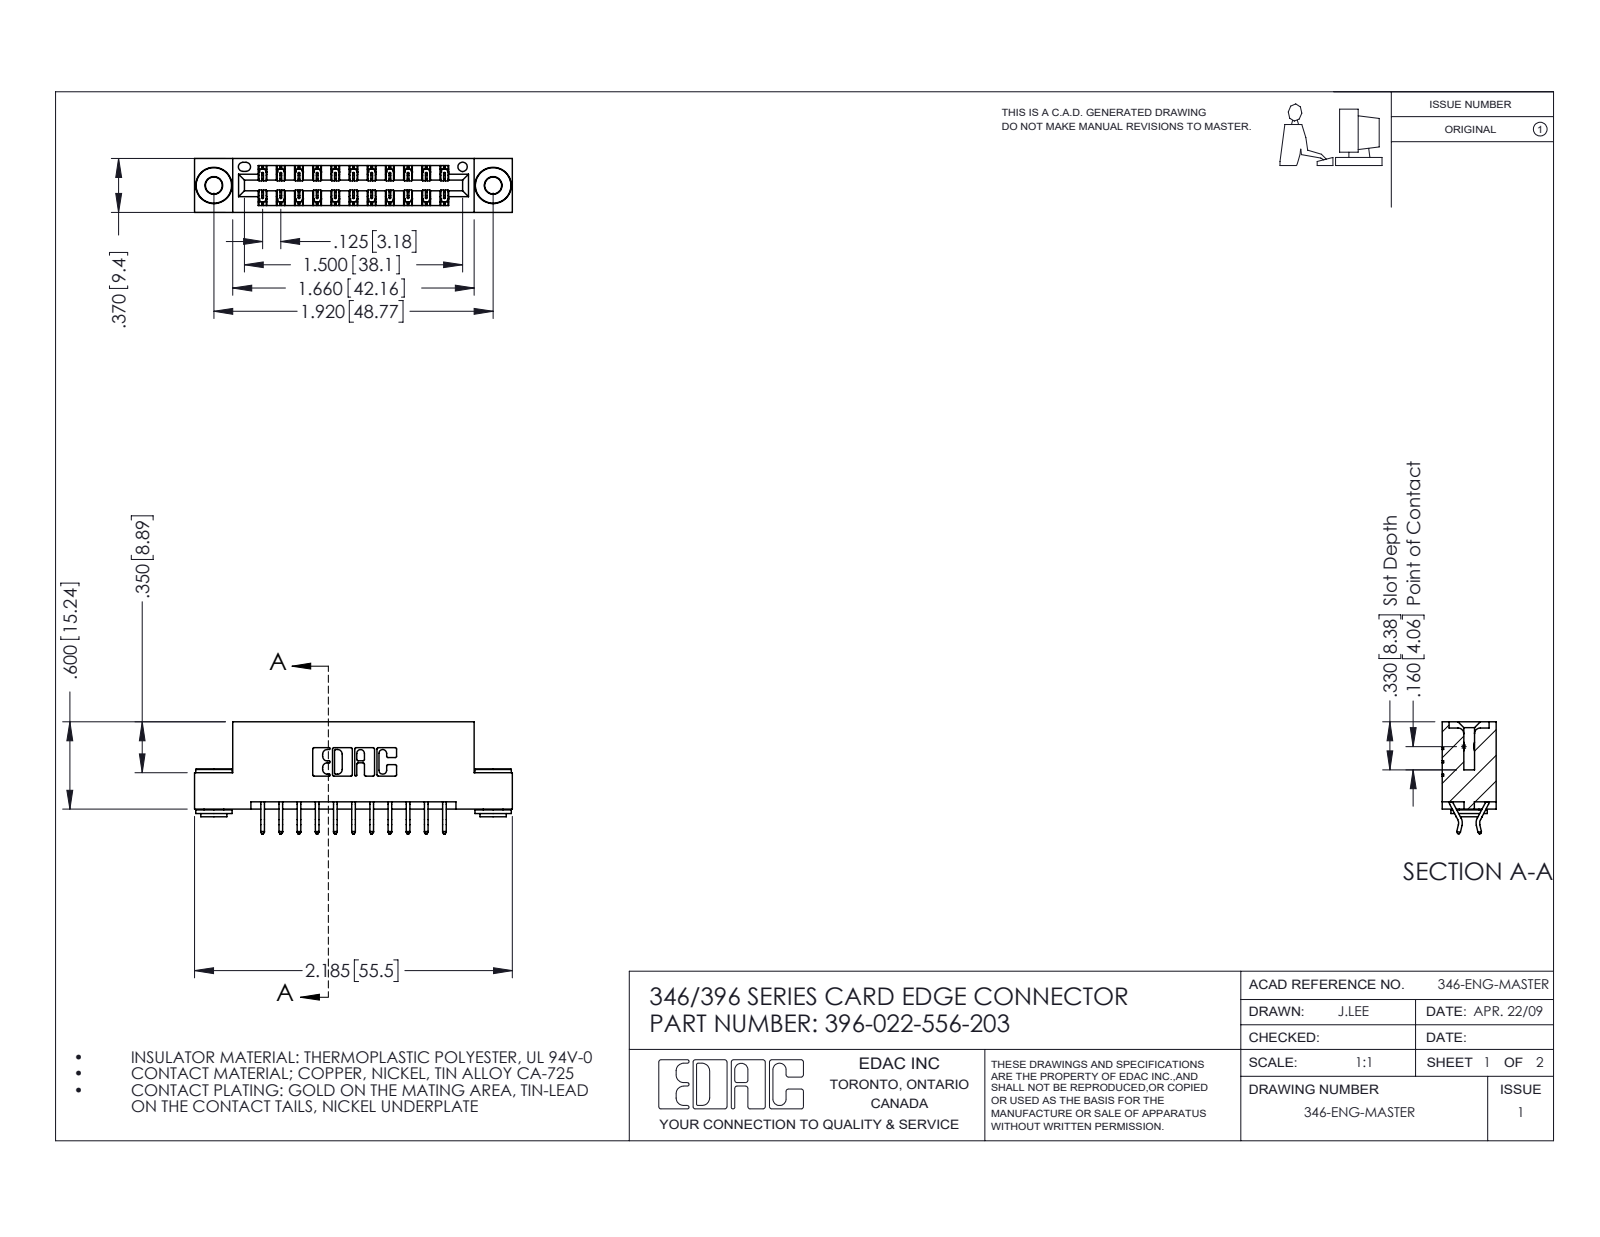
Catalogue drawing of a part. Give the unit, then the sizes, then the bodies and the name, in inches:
Units: inches
Overall size (bounding box): 2.185 × 0.77 × 0.37
Round holes (diameter × count): ⌀0.116 ×2, ⌀0.156 ×2, ⌀0.064 ×1
Round bosses / shafts (diameter × count): ⌀0.25 ×2, ⌀0.18 ×2, ⌀0.136 ×2
Partial cylindrical surfaces — rounded edges, fillets, slot ends (radius × count): R0.006 ×33, R0.01 ×22, R0.007 ×6, R0.031 ×6, R0.026 ×3, R0.01 ×2, R0.014 ×2, R0.022 ×2
Main face-to-face distances: 0.25, 0.048, 0.322, 0.37, 0.025, 0.072, 0.298, 0.275, 0.148, 0.222
Hole centre spacings: 0.246, 1.715, 1.92
Volume: 0.317 in³ · Surface area: 10.6 in²
Bodies: 25 solids, 1436 faces (944 planar, 484 cylindrical, 8 other)
Part name (STEP PRODUCT): 396-022-556-203; 346 Part_Flush Mounting Lugs - 0.156 Dia-TH; 345-250-002_345-250-002-102; 345-292-001_556 Tail
STEP written by: SolidWorks 2016 (CONFIG_CONTROL_DESIGN)
